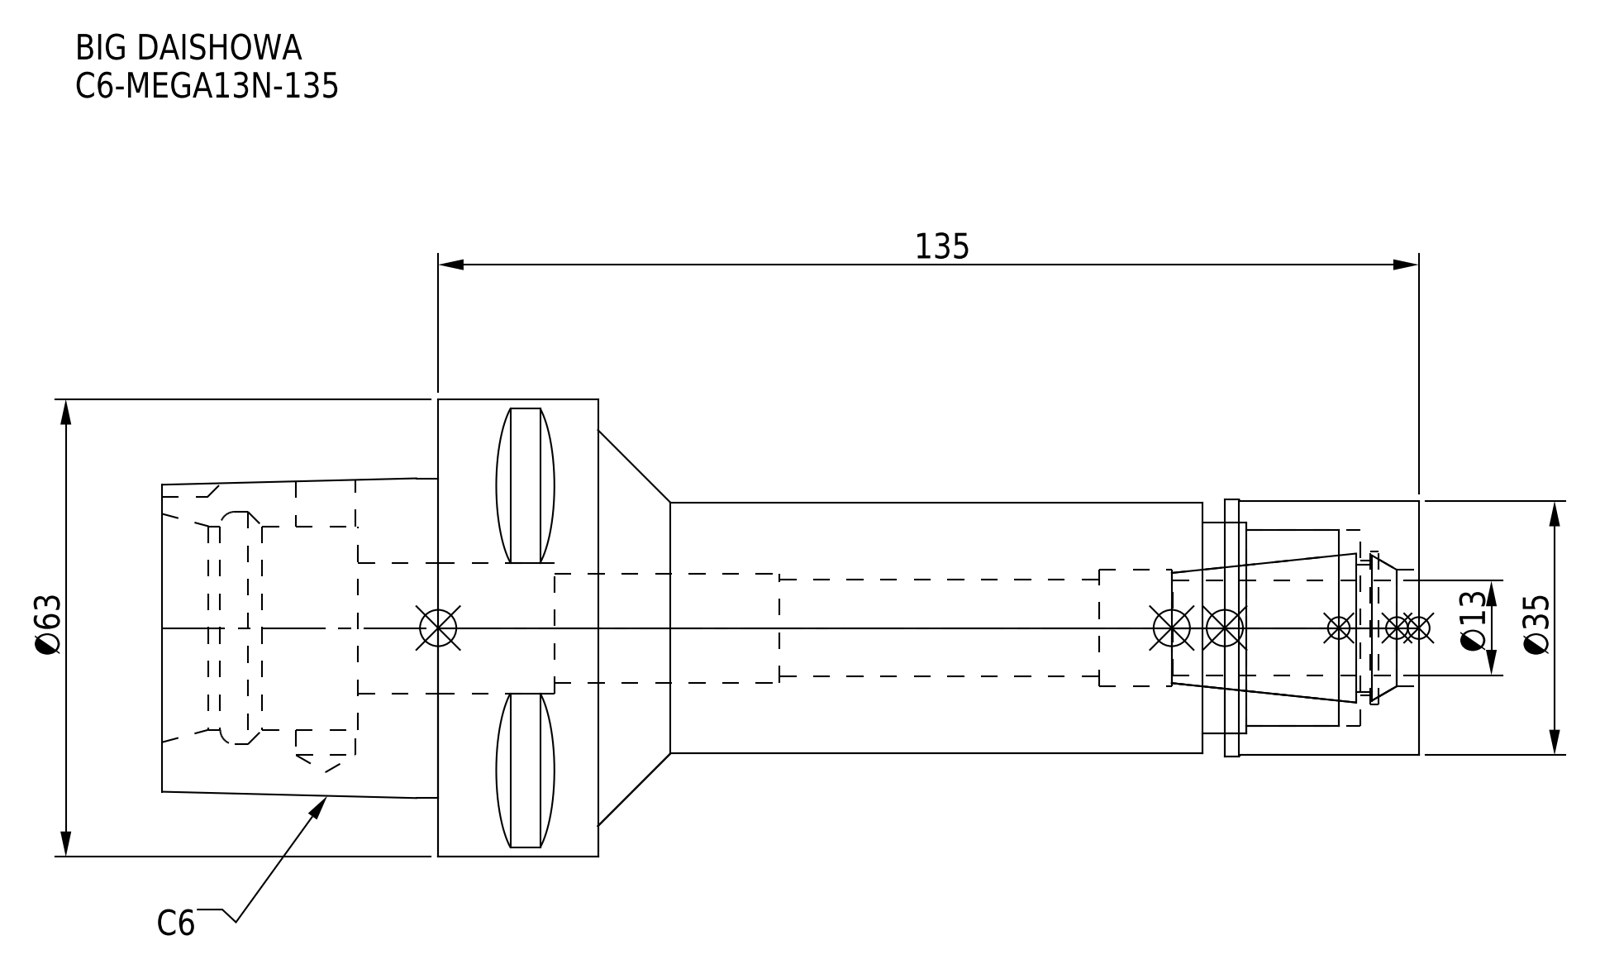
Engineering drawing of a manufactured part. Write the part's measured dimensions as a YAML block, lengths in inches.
part_name: "DXF_TEMP_ASSY_ASM_4_ASM.stp; C6-MEGA13N-135-130-FreeParts; MGN13_1.stp; C6-MEGA13N-135-130.stp (+3 more)"
step_written_by: "SolidWorks 2019 (CONFIG_CONTROL_DESIGN)"
units: inches
bodies: {solids: 2, faces: 98, planar: 39, cylindrical: 41, other: 18}
overall_size: [6.811, 2.48, 2.48]
volume: 11.33
surface_area: 64.52
round_holes:
  - {diameter: 0.319, count: 1}
  - {diameter: 0.524, count: 1}
  - {diameter: 0.591, count: 1}
  - {diameter: 0.63, count: 1}
  - {diameter: 0.709, count: 1}
  - {diameter: 0.728, count: 1}
  - {diameter: 0.827, count: 1}
  - {diameter: 1.063, count: 1}
  - {diameter: 1.102, count: 1}
  - {diameter: 1.142, count: 1}
  - {diameter: 1.26, count: 1}
round_bosses_or_shafts:
  - {diameter: 2.48, count: 1}
  - {diameter: 1.39, count: 1}
  - {diameter: 1.378, count: 1}
  - {diameter: 1.358, count: 1}
partial_cylinders:
  - {radius: 0.197, count: 1}
face_to_face_distances: [5.315, 0.866, 4.449, 0.433, 6.811, 2.362, 1.496, 1.063, 1.299, 5.748]
